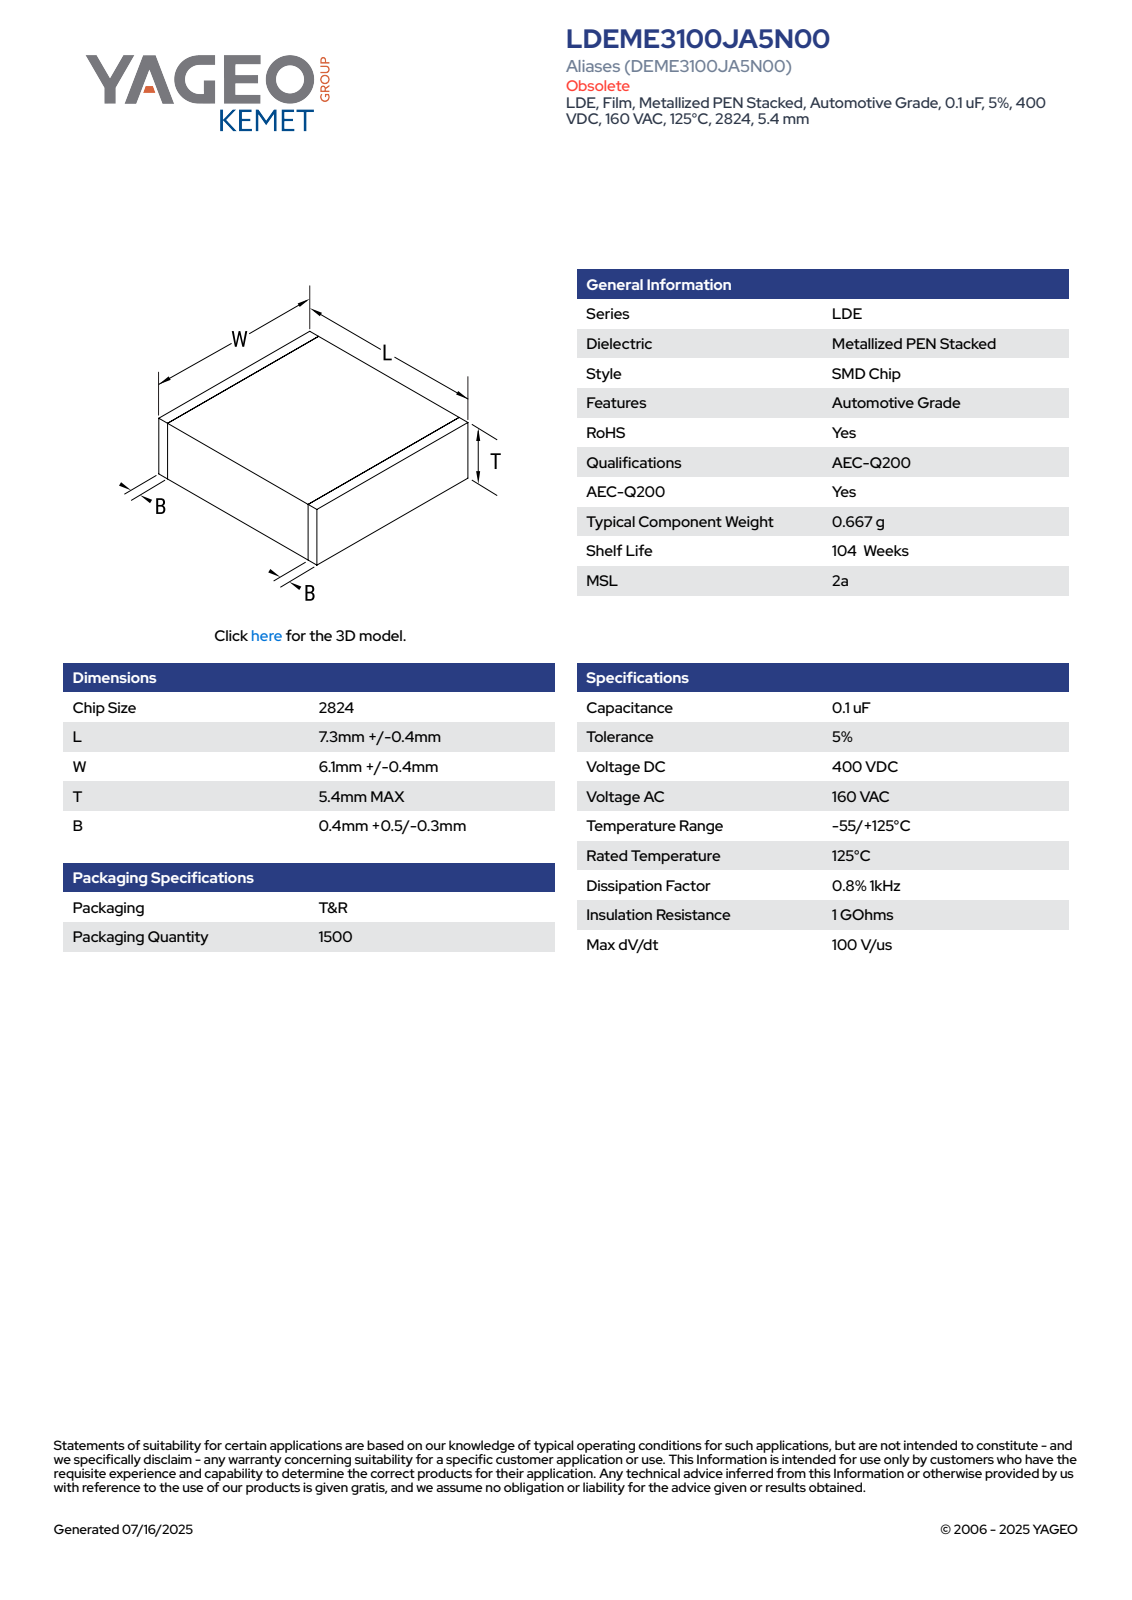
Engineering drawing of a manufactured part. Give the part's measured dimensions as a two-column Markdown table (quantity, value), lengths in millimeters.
| quantity | value |
| --- | --- |
| part name | CFS_LDELDB_2824_L7.7W6.5T5.4B0.9 |
| STEP written by | SolidWorks 2020 (AUTOMOTIVE_DESIGN) |
| units | millimeters |
| bodies | 4 solids, 73 faces (73 planar, 0 cylindrical, 0 other) |
| overall size | 7.7 × 6.5 × 5.4 |
| volume | 269 mm³ |
| surface area | 256 mm² |
| main face-to-face distances | 5.38, 6.48, 7.7, 5.39, 6.49, 5.4, 6.5, 0.5, 7.2, 6.7 |
